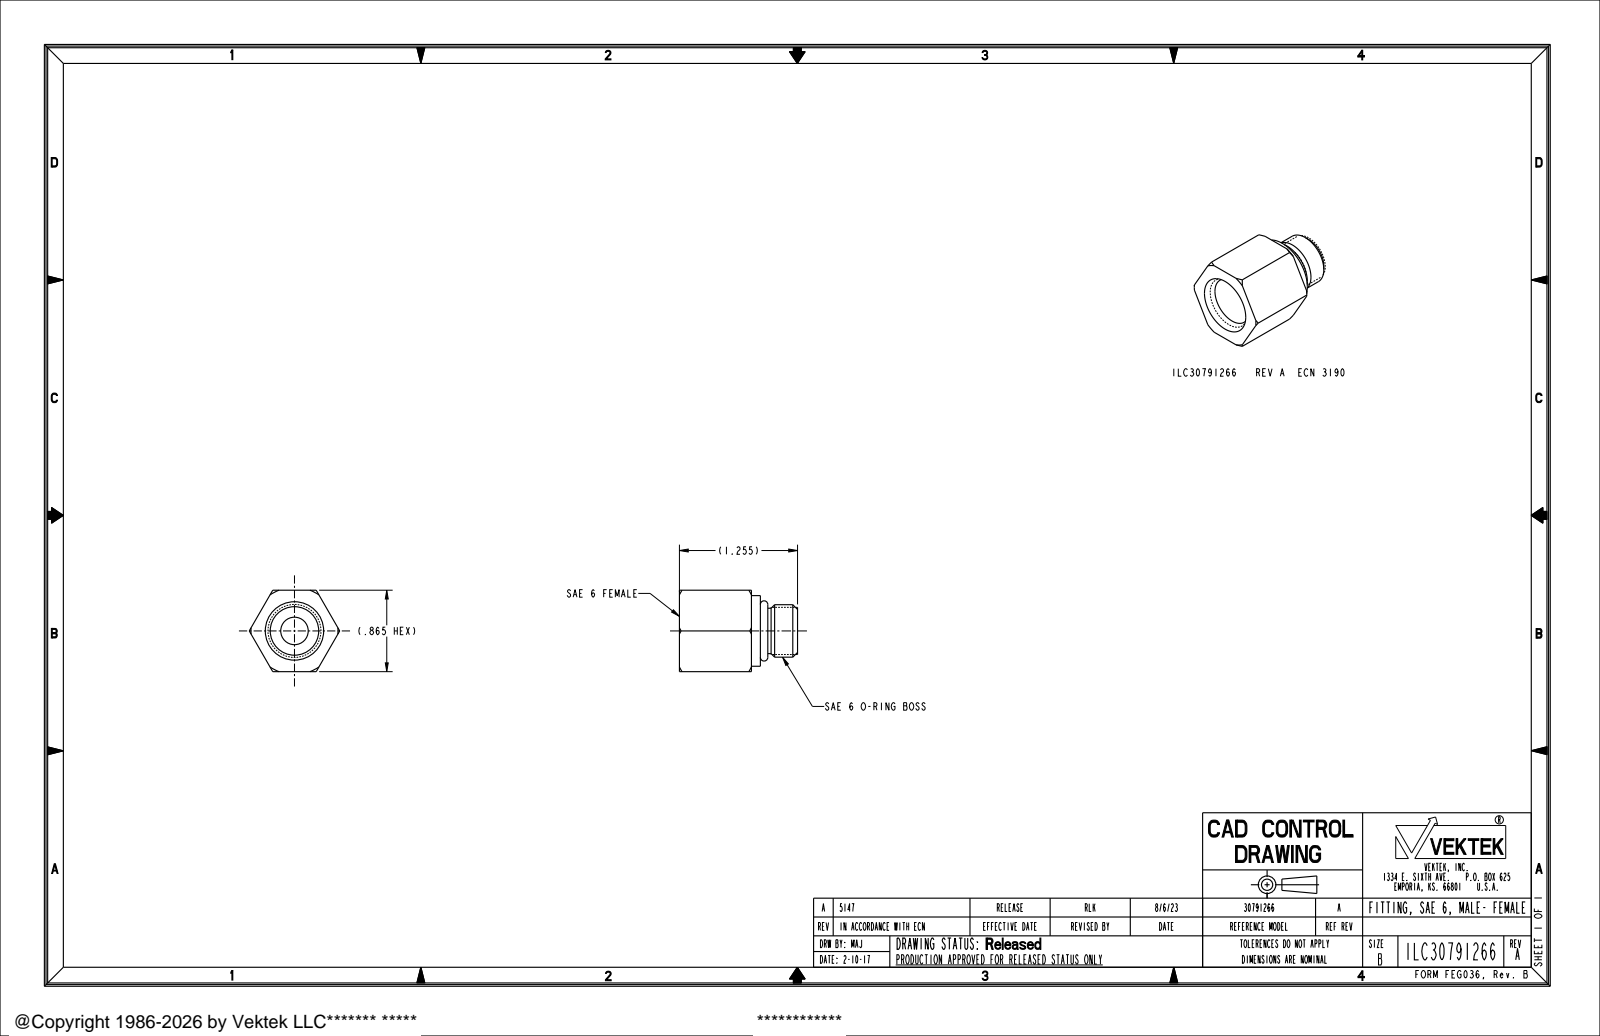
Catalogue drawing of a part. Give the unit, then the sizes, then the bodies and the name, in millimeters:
Units: millimetres
Overall size (bounding box): 31.9 × 24.4 × 22
Round holes (diameter × count): ⌀7.4 ×1, ⌀13.1 ×1
Round bosses / shafts (diameter × count): ⌀19.1 ×1, ⌀14.3 ×1, ⌀14.1 ×1, ⌀12.7 ×1, ⌀12.2 ×1
Main face-to-face distances: 21.1, 22, 21.8, 2.4, 19.4, 10, 12.4, 31.9
Volume: 7 030 mm³ · Surface area: 4 745 mm²
Bodies: 1 solid, 46 faces (10 planar, 14 cylindrical, 22 other)
Part name (STEP PRODUCT): ILC30791266
STEP written by: CREO PARAMETRIC BY PTC INC, 2021164 (AUTOMOTIVE_DESIGN)
